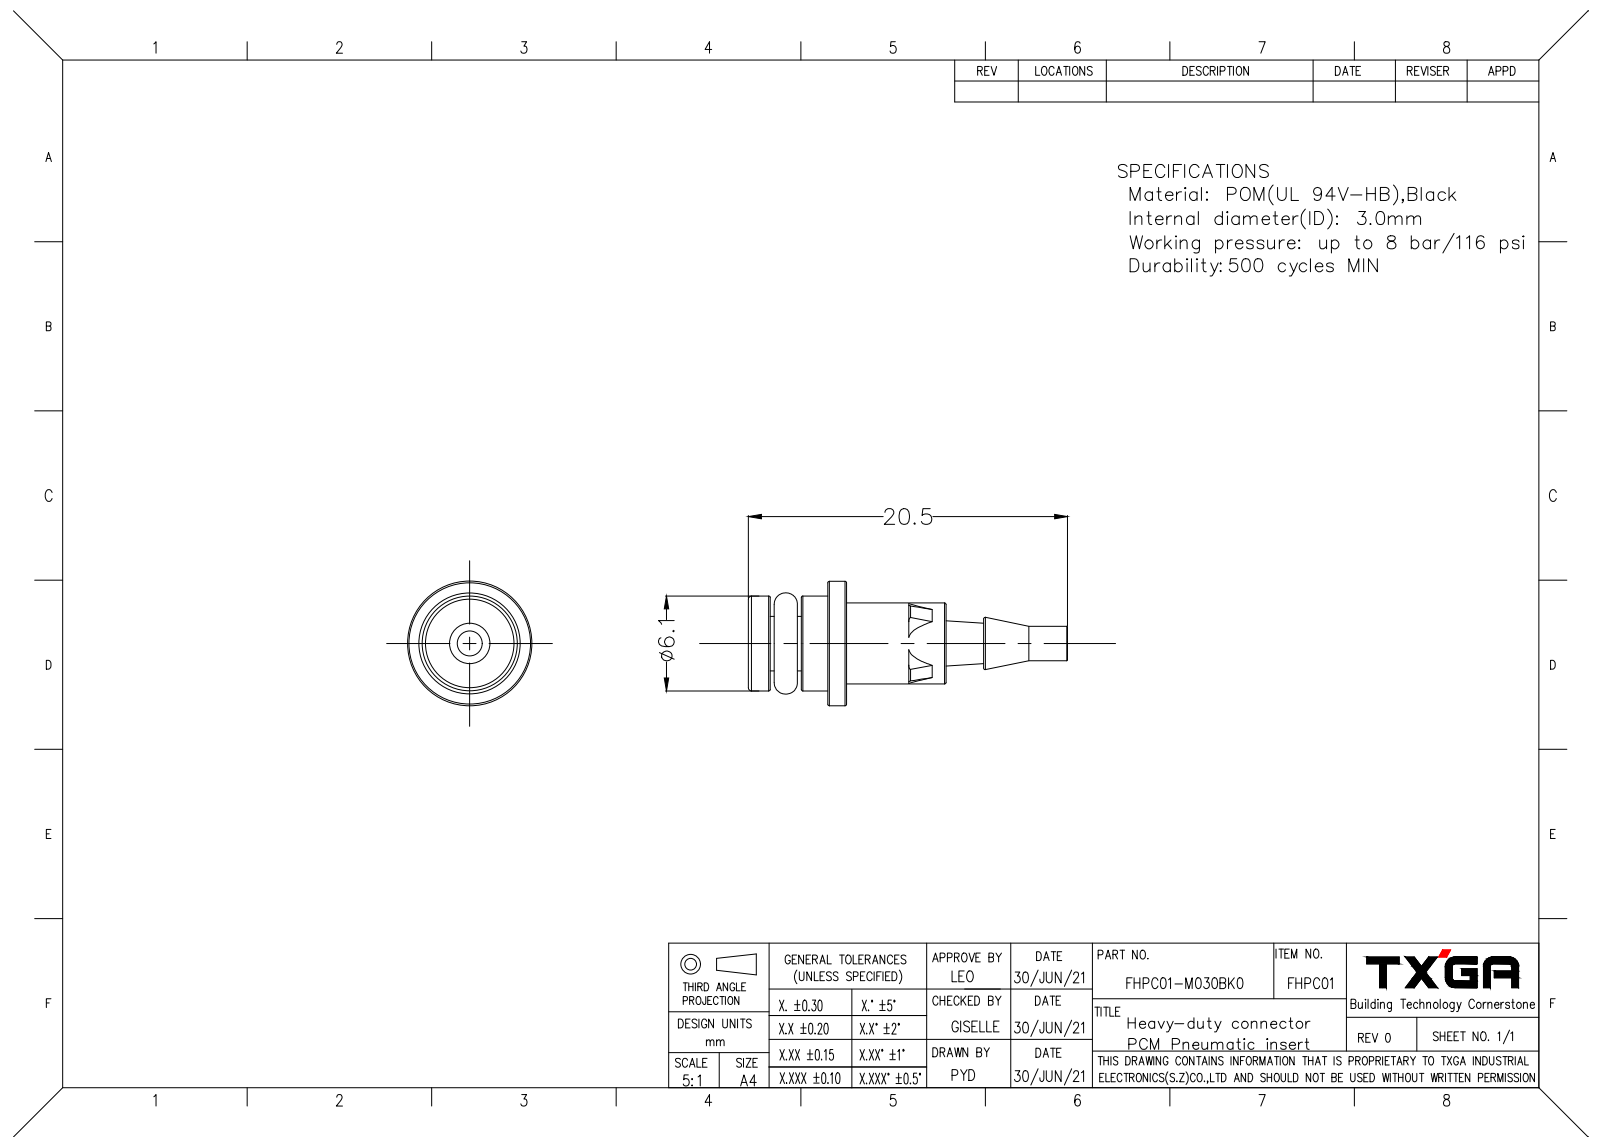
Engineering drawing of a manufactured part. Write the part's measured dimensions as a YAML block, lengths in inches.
part_name: "Admi16F8F3C4yupv"
step_written_by: "SIEMENS PLM Software NX 10.0 (AUTOMOTIVE_DESIGN)"
units: inches
bodies: {solids: 1, faces: 46, planar: 20, cylindrical: 8, other: 18}
overall_size: [0.799, 0.315, 0.315]
volume: 0.02
surface_area: 0.866
round_holes:
  - {diameter: 0.059, count: 1}
  - {diameter: 0.102, count: 1}
round_bosses_or_shafts:
  - {diameter: 0.315, count: 1}
  - {diameter: 0.244, count: 1}
  - {diameter: 0.209, count: 1}
  - {diameter: 0.197, count: 1}
face_to_face_distances: [0.201, 0.248, 0.047, 0.504, 0.303, 0.256, 0.132, 0.069, 0.116, 0.372]
